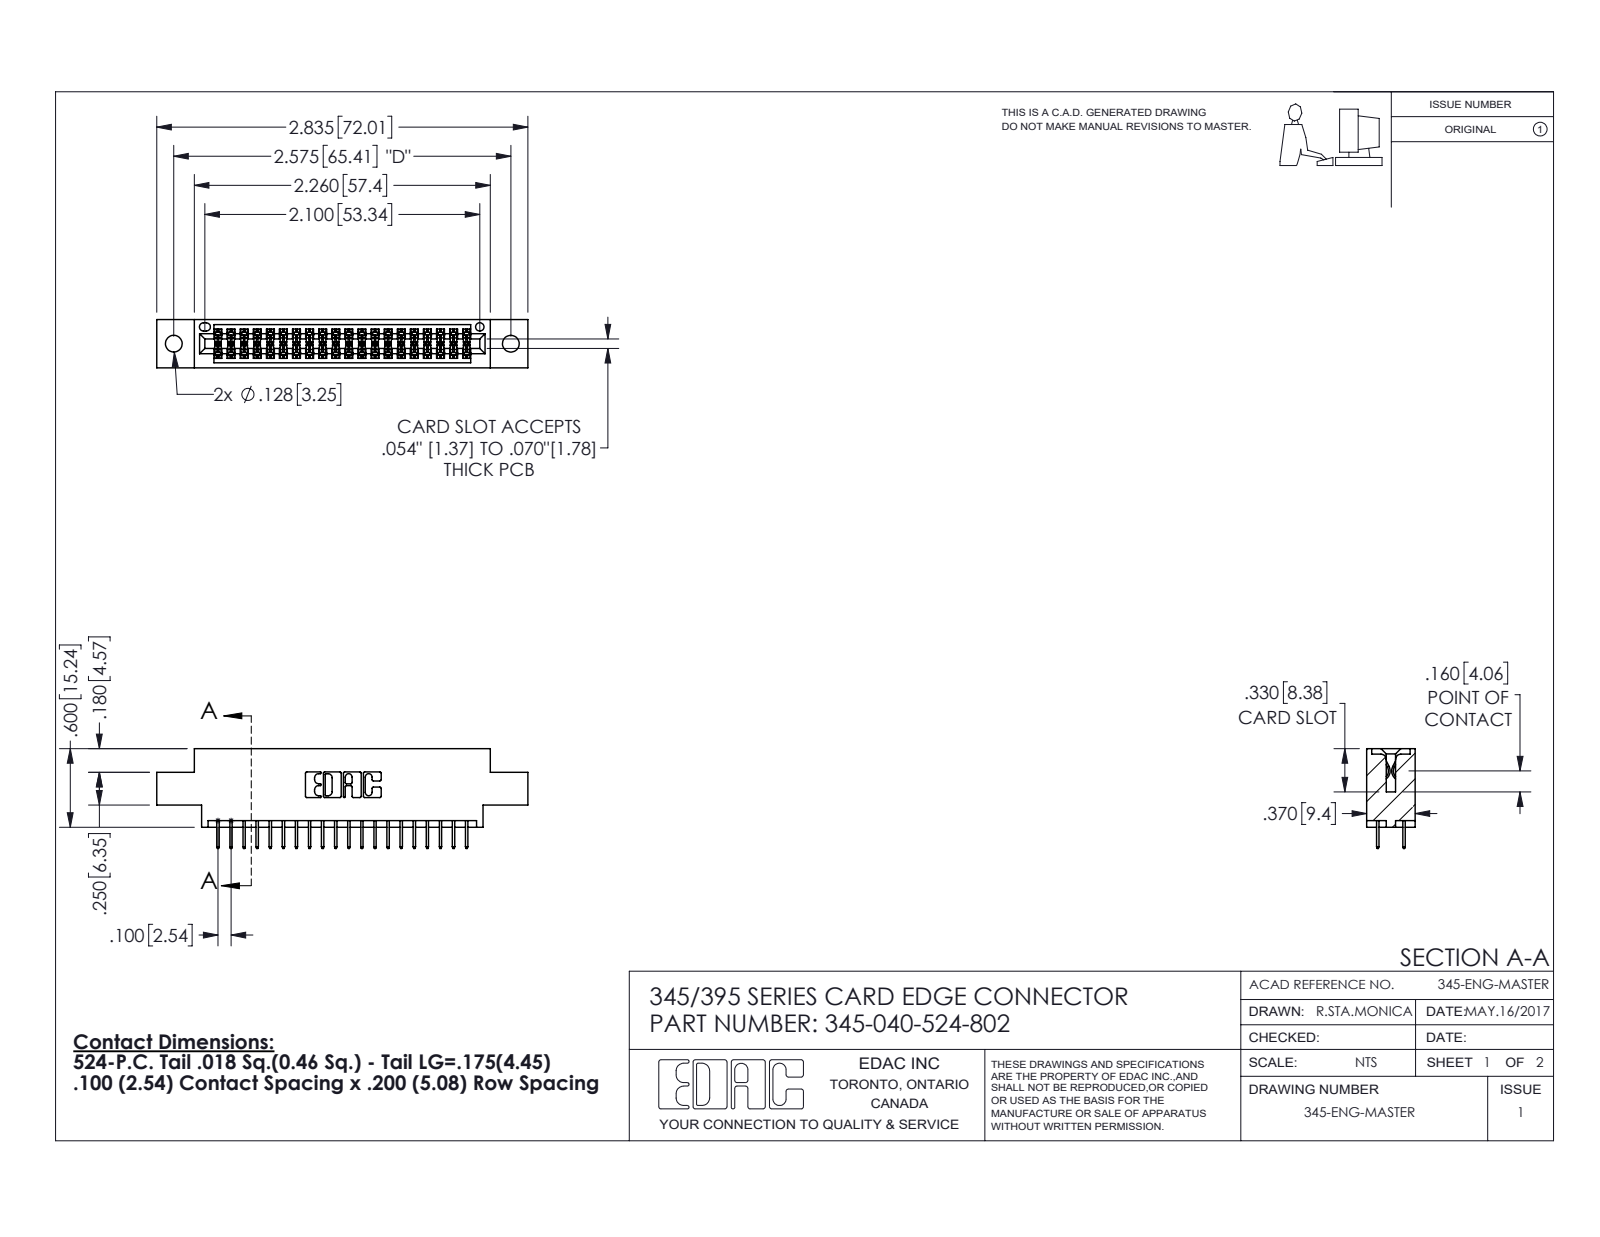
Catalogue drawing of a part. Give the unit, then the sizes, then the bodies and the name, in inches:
Units: inches
Overall size (bounding box): 2.835 × 0.762 × 0.37
Round holes (diameter × count): ⌀0.128 ×2, ⌀0.064 ×1
Partial cylindrical surfaces — rounded edges, fillets, slot ends (radius × count): R0.006 ×60, R0.01 ×22, R0.007 ×6, R0.031 ×6, R0.026 ×3, R0.014 ×2, R0.019 ×2, R0.022 ×2
Main face-to-face distances: 0.072, 0.298, 0.37, 0.2, 0.098, 0.272, 0.025, 0.225, 0.175, 0.072
Hole centre spacings: 0.27, 2.341, 2.575
Volume: 0.402 in³ · Surface area: 13.97 in²
Bodies: 41 solids, 2290 faces (1644 planar, 646 cylindrical, 0 other)
Part name (STEP PRODUCT): 345-040-524-802; 345-292-001_345-293-124; 345 Part_0.170 Offset - 0.128 Dia
STEP written by: SolidWorks 2016 (CONFIG_CONTROL_DESIGN)
